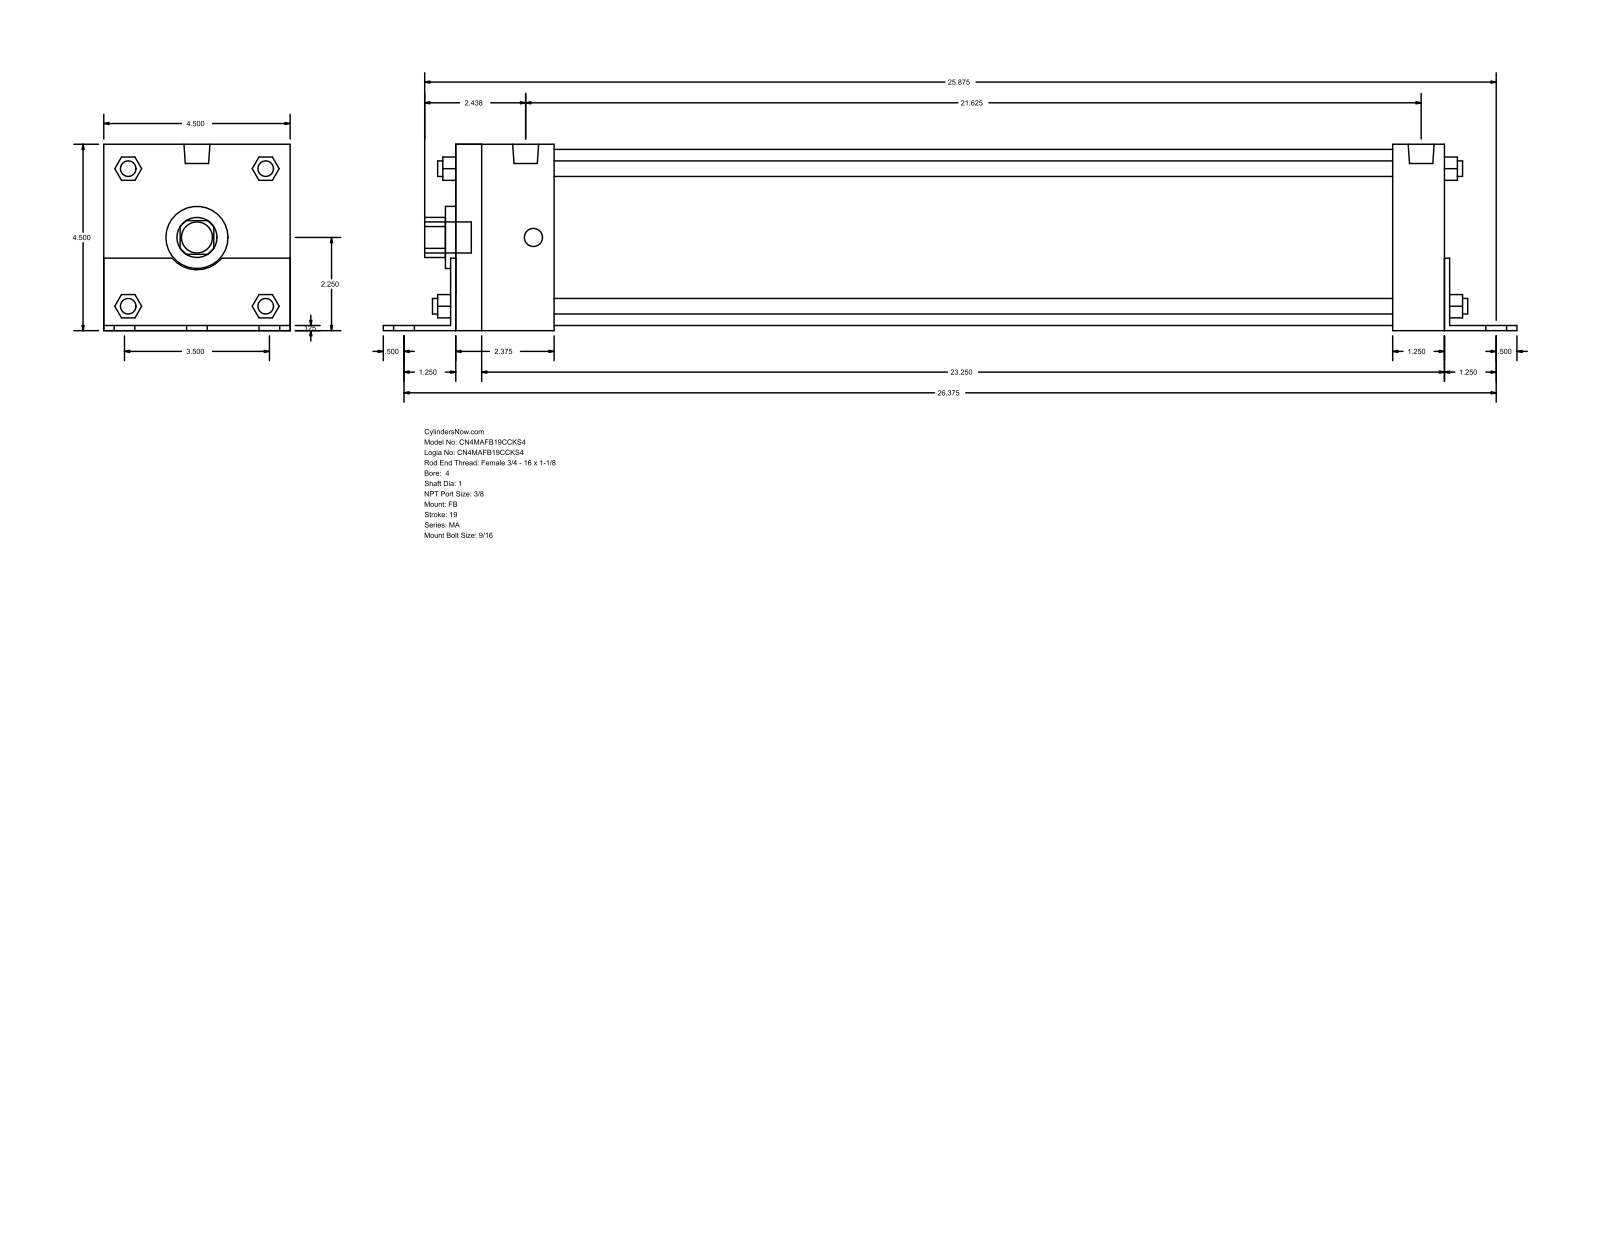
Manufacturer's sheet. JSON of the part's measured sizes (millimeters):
{"part_name": "MA_FB__0400_1", "step_written_by": "GSSL Pune (CONFIG_CONTROL_DESIGN)", "units": "millimeters", "bodies": {"solids": 0, "faces": 140, "planar": 105, "cylindrical": 35, "other": 0}, "overall_size": [695.33, 114.35, 114.3], "round_holes": [[25.4, 1], [38.1, 1], [107.95, 1]], "round_bosses_or_shafts": [[14.29, 6], [11.11, 4], [9.53, 4], [15.93, 2], [19.05, 1]], "partial_cylinders_radius": [[12.29, 1], [19.81, 1]], "face_to_face_distances": [114.3, 3.17, 114.35, 609.6, 3.12, 111.18, 606.43, 612.77, 577.85, 574.68]}
